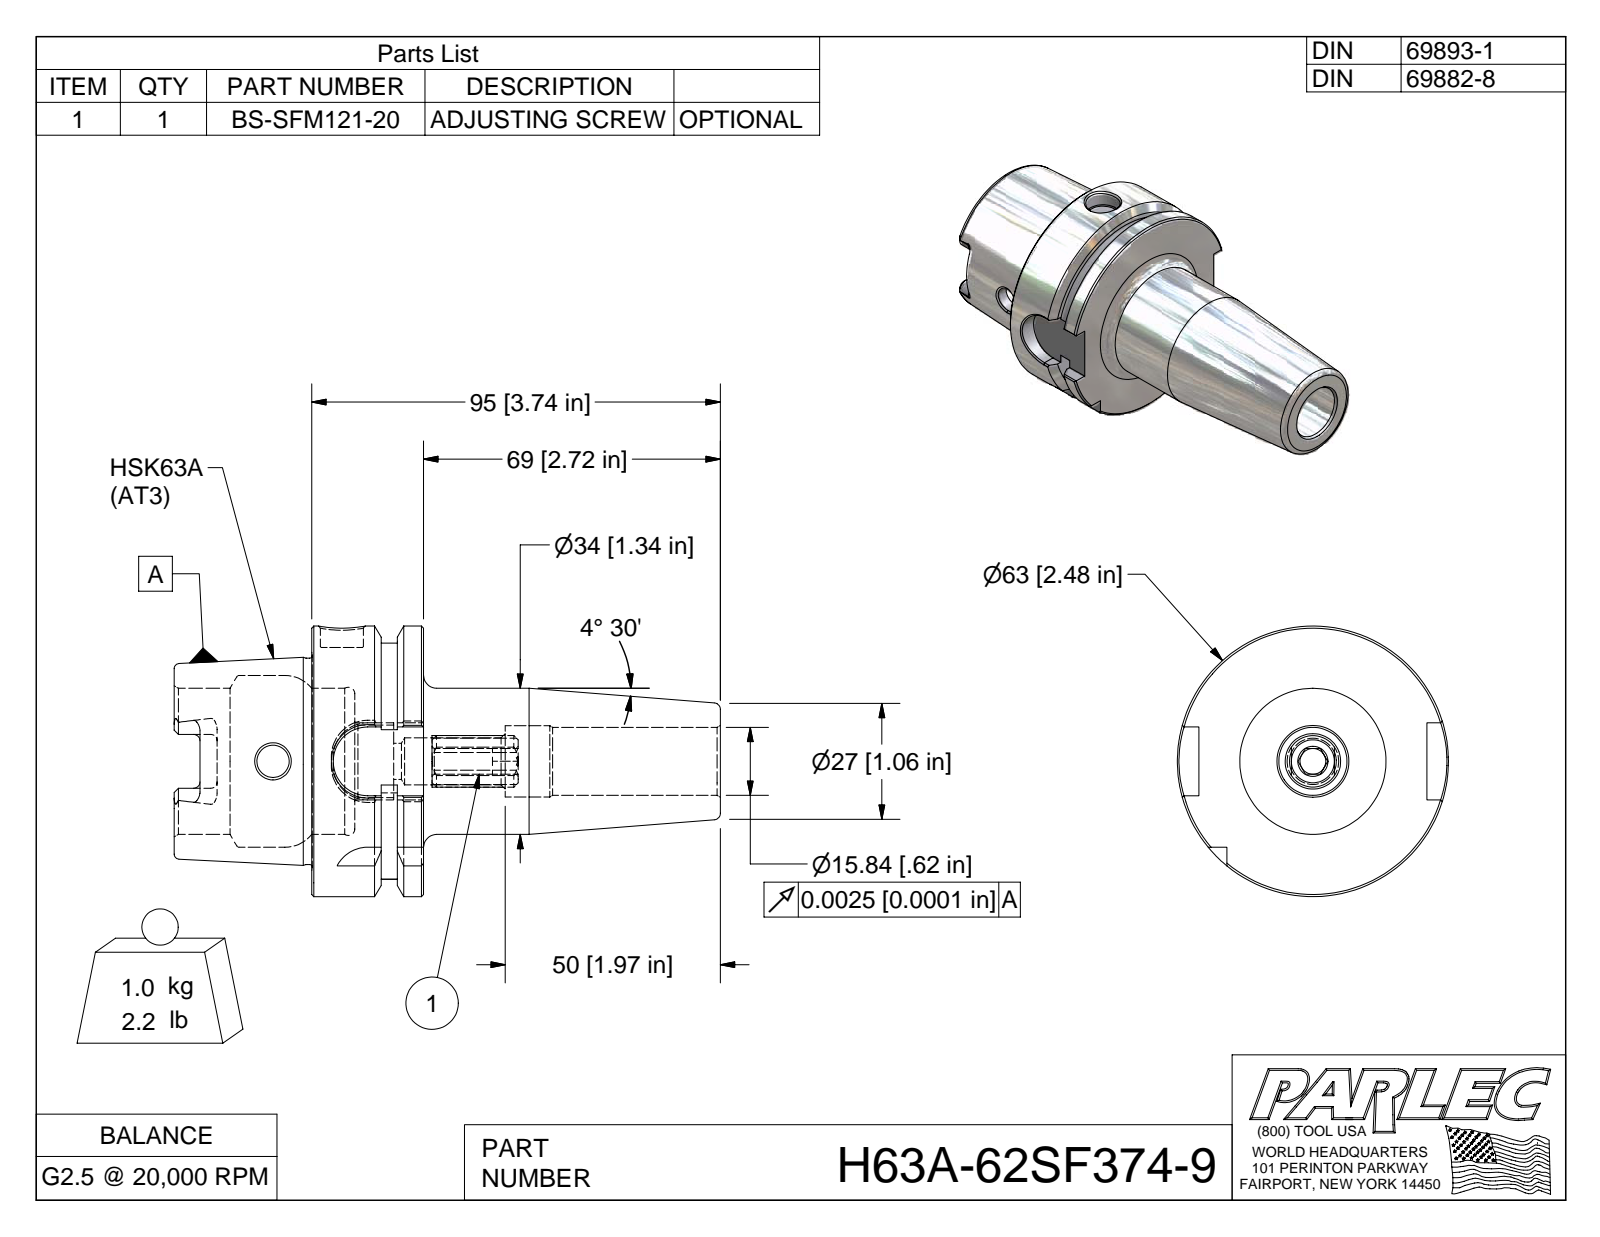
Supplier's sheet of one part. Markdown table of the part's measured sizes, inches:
| quantity | value |
| --- | --- |
| part name | H63A-62SF374-9; H63A-62SF374-9-1; BS-SFM121-20 |
| STEP written by | Autodesk Inventor 2009 (AUTOMOTIVE_DESIGN) |
| units | inches |
| bodies | 2 solids, 157 faces (58 planar, 35 cylindrical, 64 other) |
| overall size | 5 × 2.48 × 2.48 |
| volume | 7.701 in³ |
| surface area | 51.28 in² |
| round holes (diameter × count) | 0.295 × 1, 0.394 × 1, 0.624 × 1, 0.654 × 1, 0.666 × 1, 1.339 × 1, 1.575 × 1 |
| round bosses / shafts (diameter × count) | 2.48 × 1, 1.891 × 1 |
| partial cylindrical surfaces (radius × count) | 0.059 × 6, 0.113 × 4, 0.315 × 4, 0.236 × 1, 1.083 × 1 |
| main face-to-face distances | 1.024, 0.394, 0.241, 0.389, 0.63, 1.26, 1.654, 2.283, 1.894, 0.635 |
